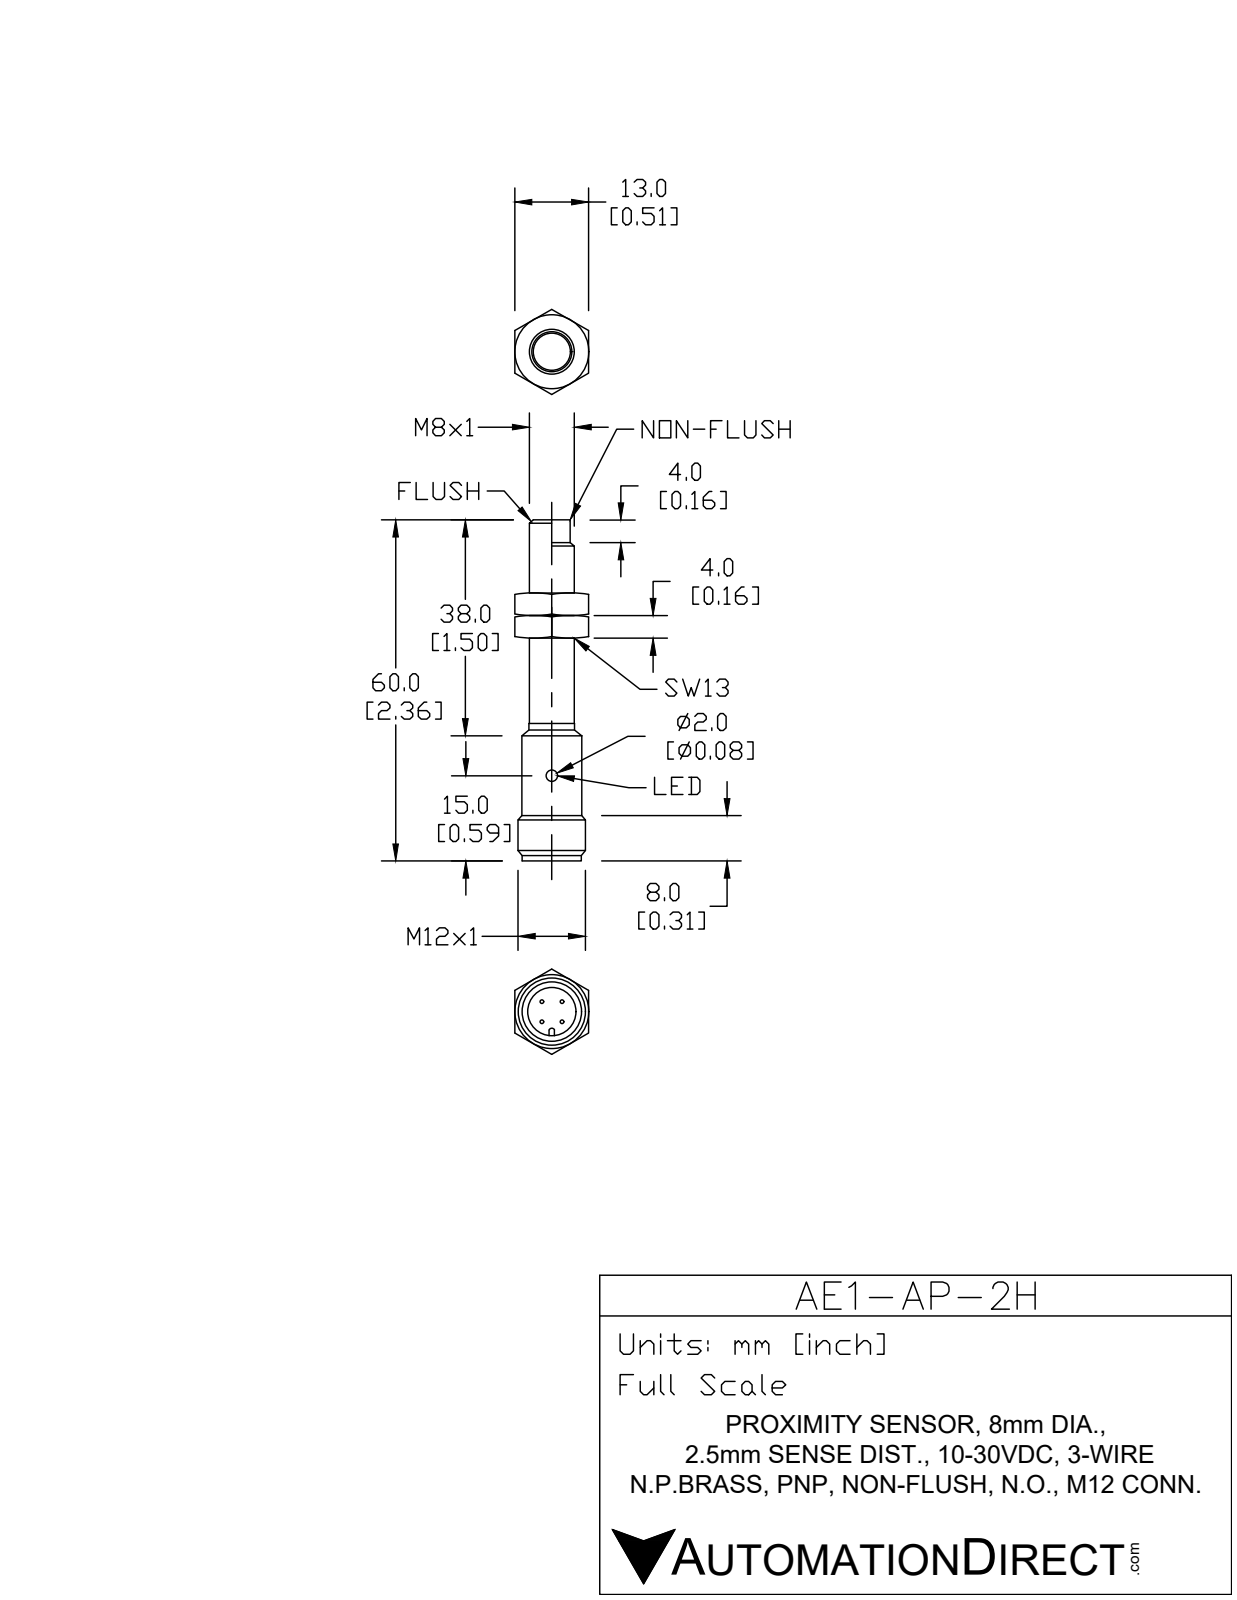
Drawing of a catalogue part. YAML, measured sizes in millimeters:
part_name: "AE1-AP-2H"
step_written_by: "SolidWorks 2017 (AUTOMOTIVE_DESIGN)"
units: millimeters
bodies: {solids: 3, faces: 113, planar: 22, cylindrical: 59, other: 32}
overall_size: [60, 12, 12]
volume: 2560
surface_area: 3414
round_holes:
  - {diameter: 2, count: 4}
  - {diameter: 8.4, count: 1}
  - {diameter: 9.8, count: 1}
round_bosses_or_shafts:
  - {diameter: 1, count: 4}
  - {diameter: 12, count: 1}
  - {diameter: 10.5, count: 1}
  - {diameter: 9.7, count: 1}
  - {diameter: 9.6, count: 1}
  - {diameter: 8, count: 1}
  - {diameter: 6.5, count: 1}
  - {diameter: 6.2, count: 1}
partial_cylinders:
  - {radius: 1.3, count: 4}
  - {radius: 0.5, count: 1}
  - {radius: 0.6, count: 1}
  - {radius: 1.3, count: 1}
  - {radius: 3.4, count: 1}
face_to_face_distances: [11.3, 33.6, 44.9, 8.9, 4, 37.6, 48.9, 1, 51.1, 47.1]
